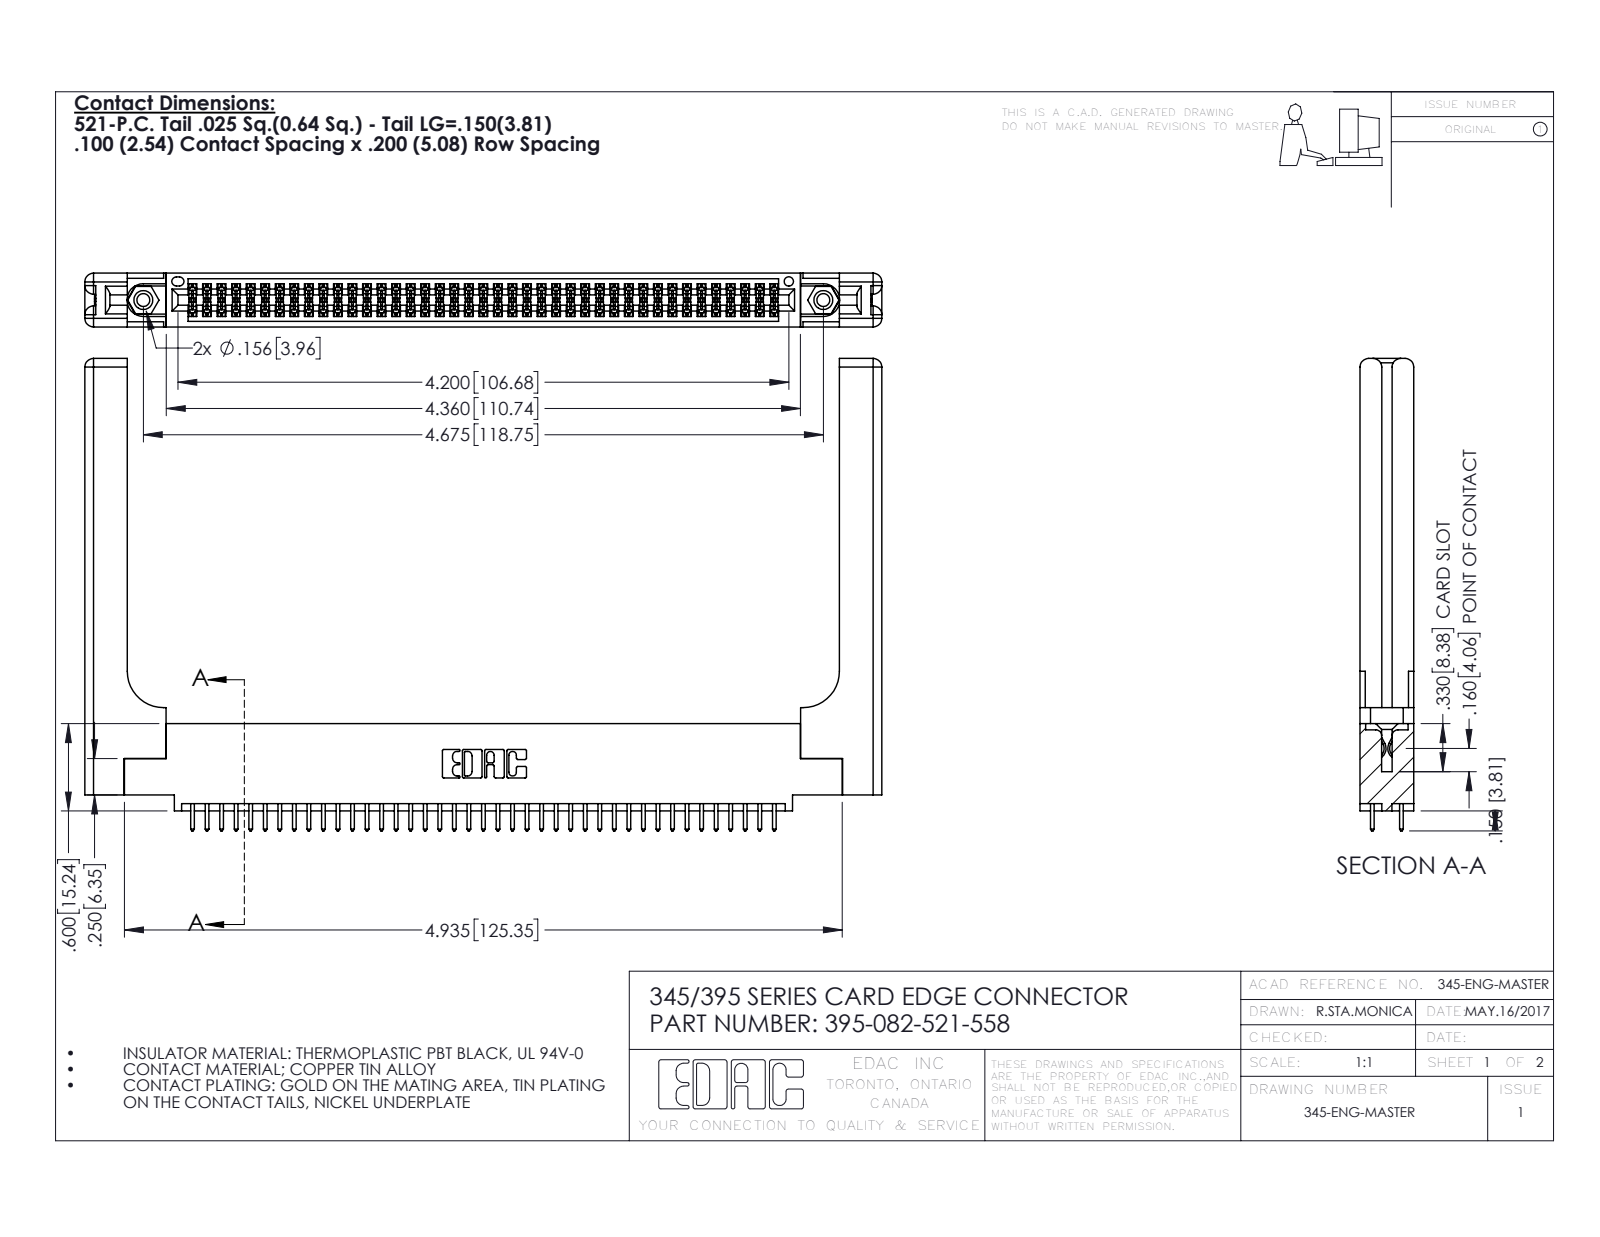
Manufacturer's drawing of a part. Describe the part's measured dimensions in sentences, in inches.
The part is named "345-292-001_345-293-121; 345-220-058_345-220-058; 345-250-001_345-250-001-102; 395-082-521-558 (+1 more)". Its 3-D file was written by "SolidWorks 2016 (CONFIG_CONTROL_DESIGN)". It is 87 solids with 4486 faces: 2938 planar, 1488 cylindrical and 60 other. Overall it measures 5.479 by 3.247 by 0.37 inches. Its volume is 1.335 cubic inches and its surface area 38.33 square inches. Round holes: 2 of diameter 0.089, 2 of diameter 0.125, 2 of diameter 0.156, 1 of diameter 0.064. Round bosses or shafts: 2 of diameter 0.155. Partial cylindrical surfaces (rounded edges, fillets, slot ends): 123 of radius 0.006, 82 of radius 0.01, 22 of radius 0.01, 16 of radius 0.06, 6 of radius 0.007, 6 of radius 0.031, 3 of radius 0.026, 2 of radius 0.014. The main face-to-face distances are 0.072, 0.298, 0.37, 0.2, 0.098, 0.272, 0.025, 0.225, 0.148, 0.15. The hole center spacings are 0.27, 4.439, 4.675.
